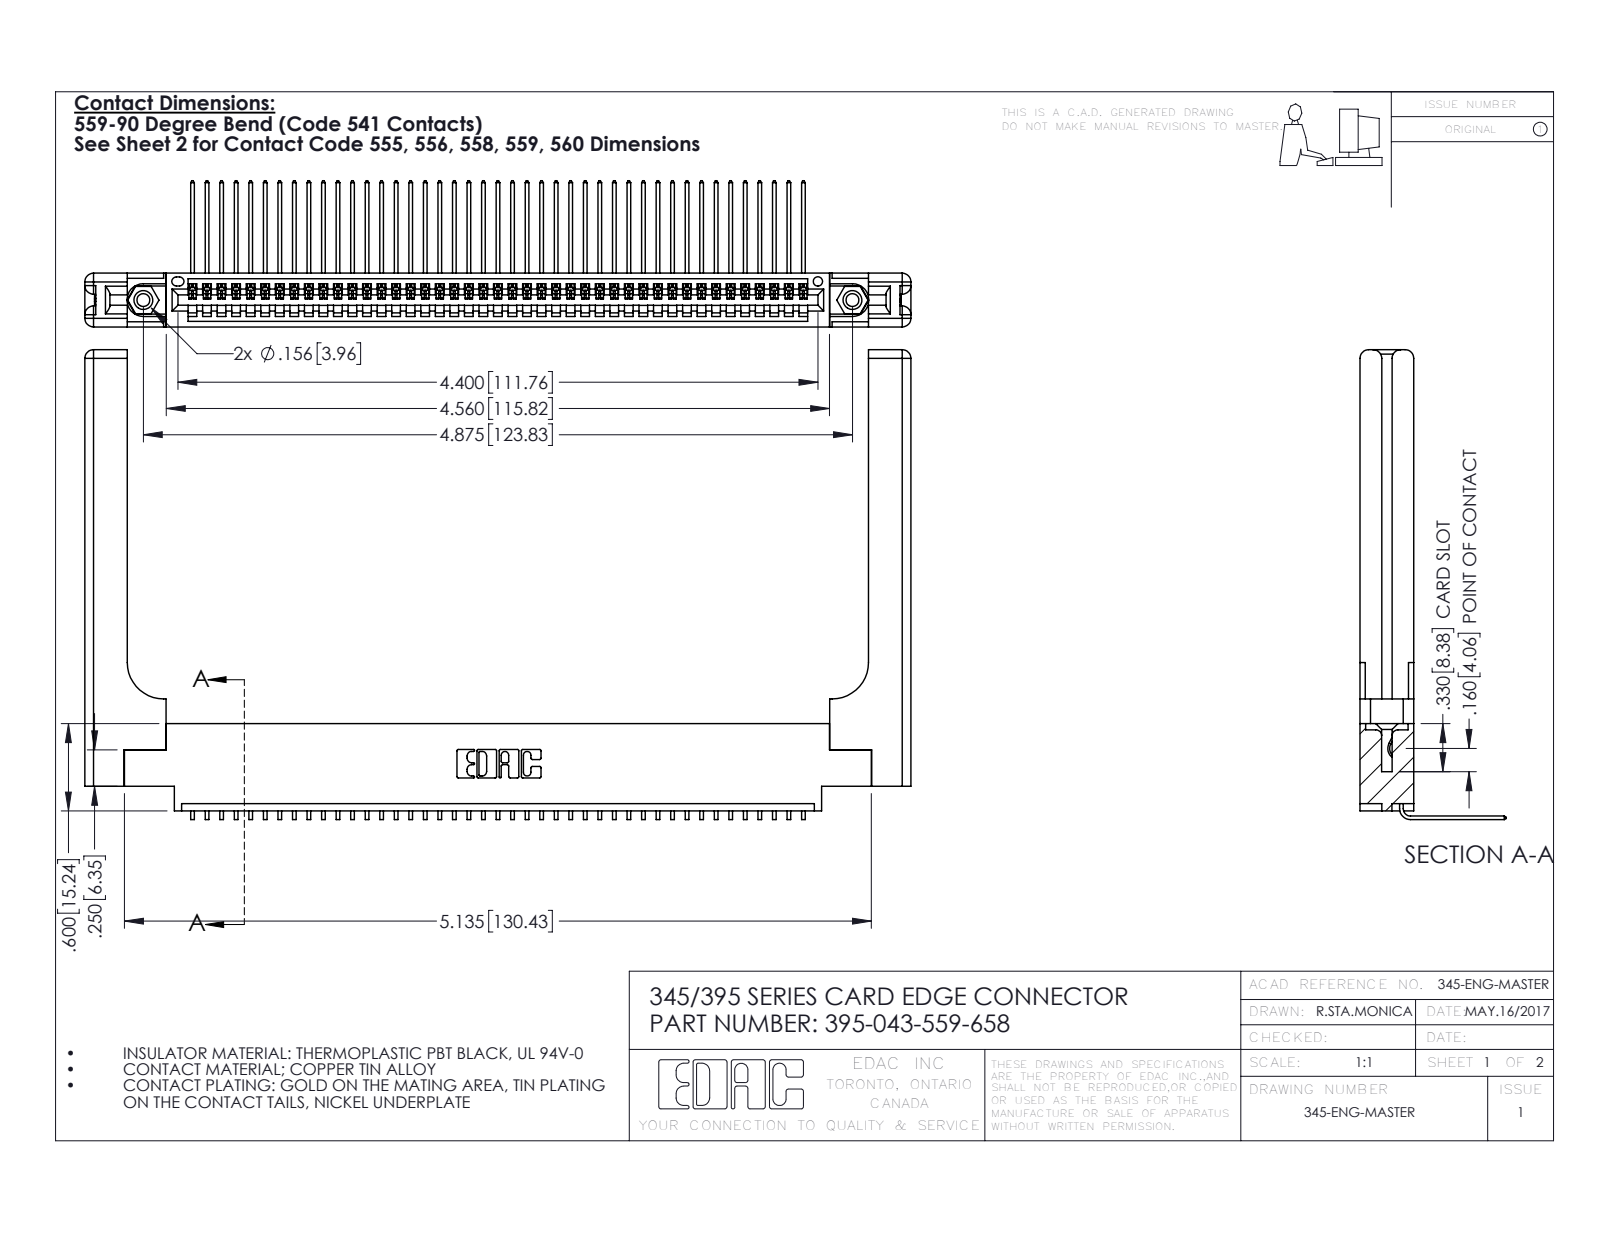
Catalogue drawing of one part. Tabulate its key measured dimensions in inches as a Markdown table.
| quantity | value |
| --- | --- |
| part name | 345 Part_0.170 Offset - 0.156 Dia-TH; 395-043-559-658; 345-220-058_345-220-058; 345-250-001_345-250-001-102 (+1 more) |
| STEP written by | SolidWorks 2016 (CONFIG_CONTROL_DESIGN) |
| units | inches |
| bodies | 48 solids, 2966 faces (2038 planar, 868 cylindrical, 60 other) |
| overall size | 5.679 × 3.229 × 1.005 |
| volume | 1.357 in³ |
| surface area | 38.05 in² |
| round holes (diameter × count) | 0.089 × 2, 0.125 × 2, 0.156 × 2, 0.064 × 1 |
| round bosses / shafts (diameter × count) | 0.155 × 2 |
| partial cylindrical surfaces (radius × count) | 0.006 × 86, 0.01 × 22, 0.06 × 16, 0.007 × 6, 0.031 × 6, 0.026 × 3, 0.03 × 2, 0.031 × 2 |
| main face-to-face distances | 0.37, 0.072, 0.298, 0.098, 0.272, 0.025, 0.2, 0.225, 0.148, 0.15 |
| hole center spacings | 0.27, 4.639, 4.875 |
